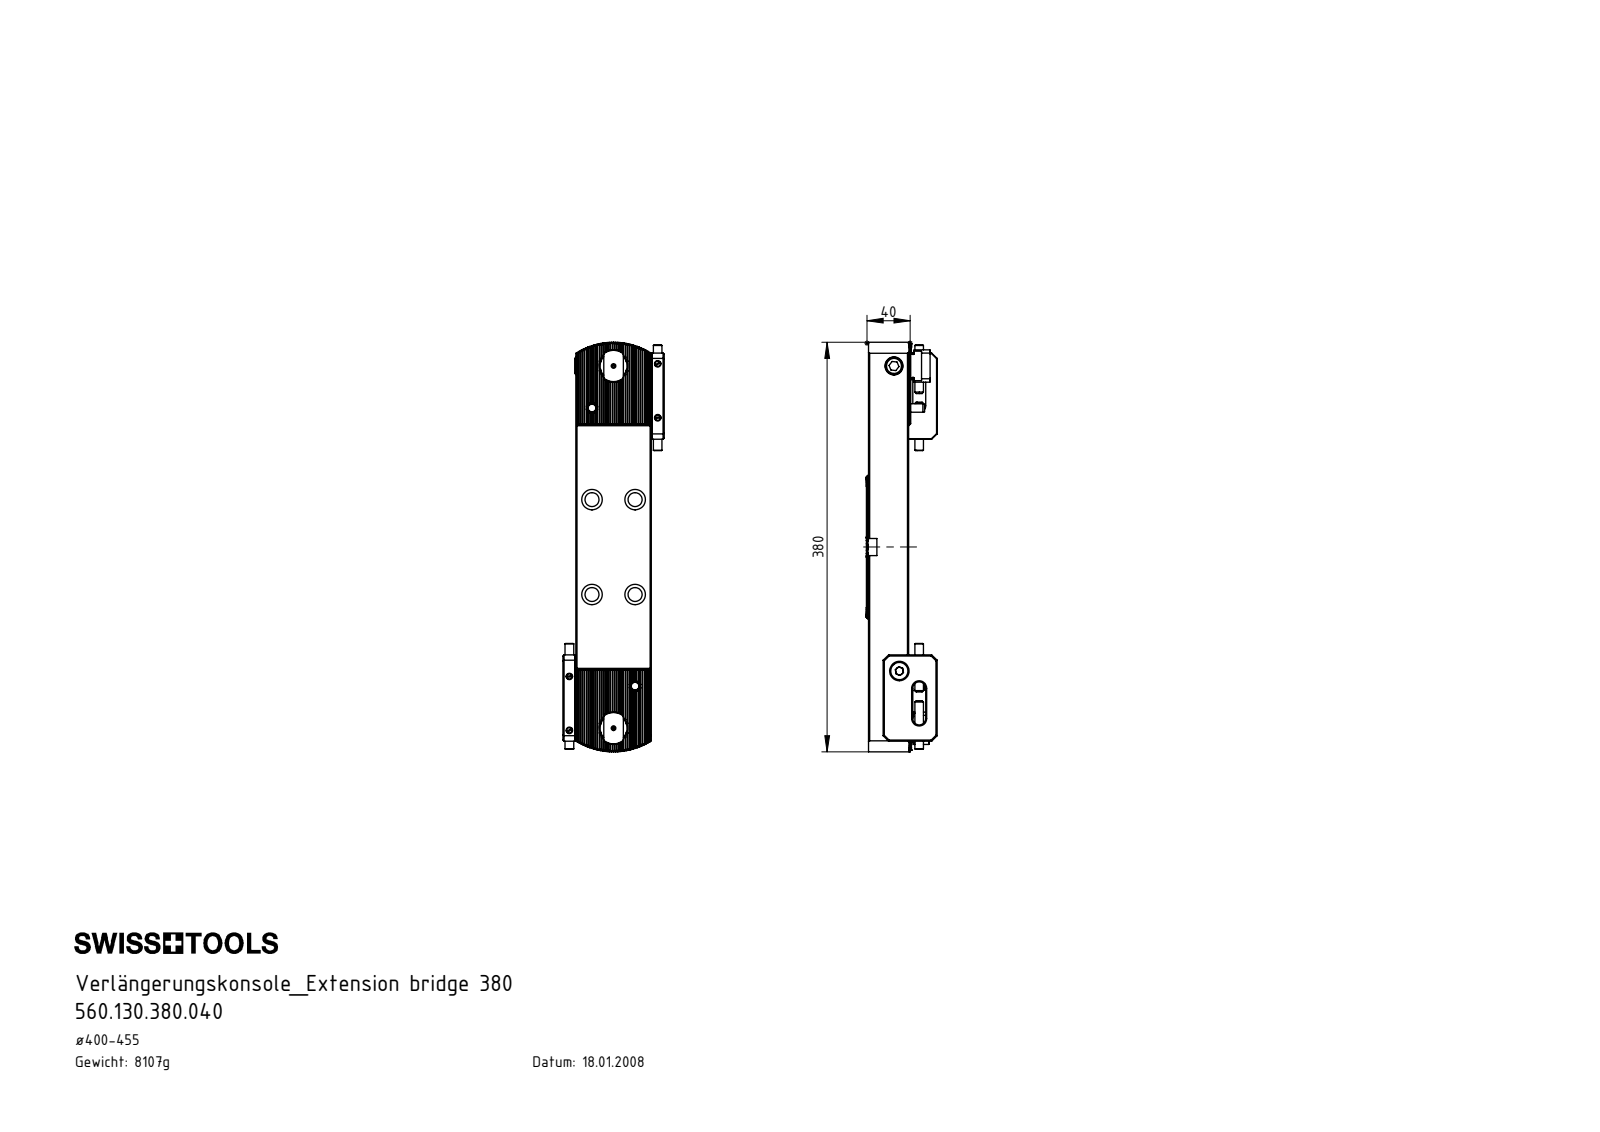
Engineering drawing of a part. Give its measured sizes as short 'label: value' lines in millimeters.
name: ISO 4026 - M8 x 45; ISO 8734 - 6 x 12; VK1-ER7.001.012_B; VK1-ER2.201.010_A_vorgespannt (+8 more)
written by: SolidWorks 2017 (CONFIG_CONTROL_DESIGN)
unit: mm
bodies: 27 solids, 1563 faces (878 planar, 402 cylindrical, 283 other)
size: 380 × 94 × 65.58
volume: 1 039 000 mm³; area: 166 218 mm²
holes: 4× ⌀5, 4× ⌀6, 4× ⌀6.8, 4× ⌀13, 4× ⌀19, 2× ⌀2, 2× ⌀8, 2× ⌀8.5, 2× ⌀10.5, 2× ⌀11, 2× ⌀14, 2× ⌀18
bosses: 4× ⌀16, 4× ⌀6, 2× ⌀10, 2× ⌀8
rounds: 66× R0.14, 8× R2, 4× R6, 2× R12.3, 2× R15, 2× R65, 1× R7.95
face distances: 37.16, 70, 12, 82, 1.73, 8.66, 3.46, 6.93, 0.5, 41.57
hole spacings: 125.6, 212.94, 336, 7.9, 18.55, 19.61, 34.53, 35.09
